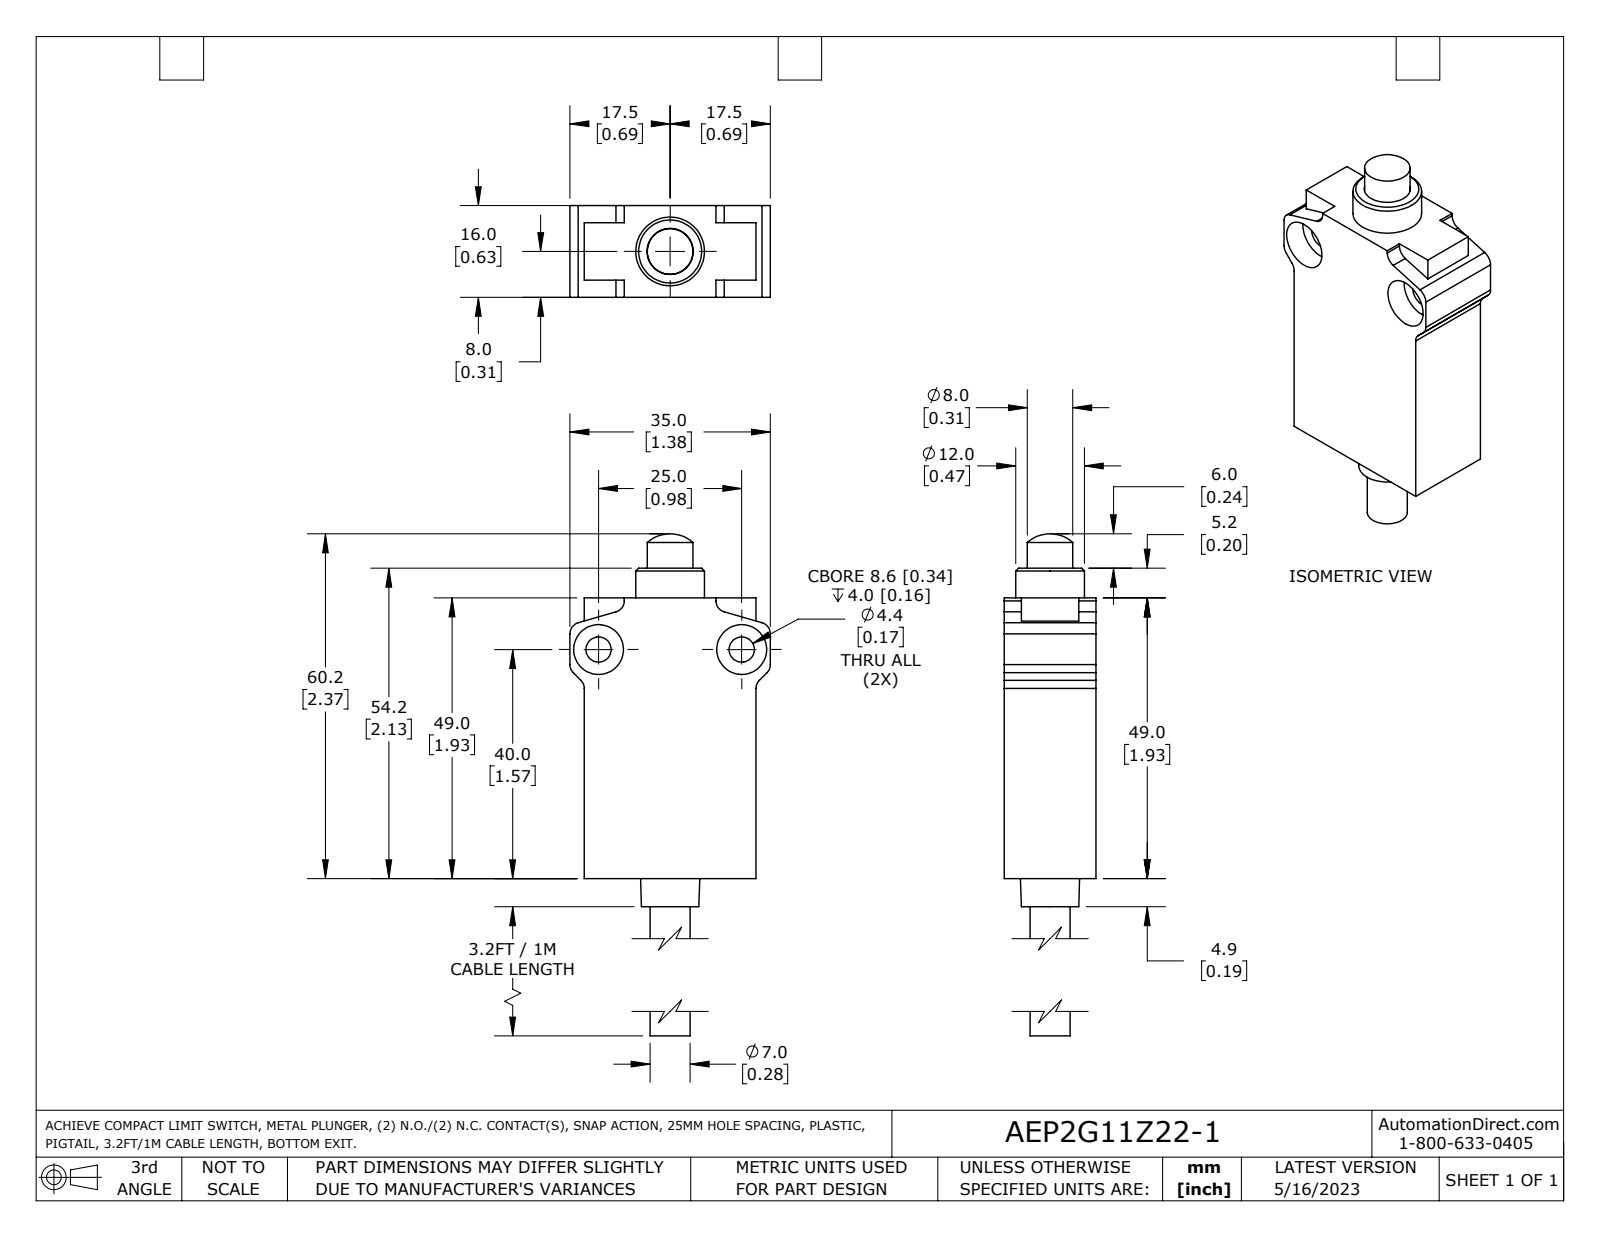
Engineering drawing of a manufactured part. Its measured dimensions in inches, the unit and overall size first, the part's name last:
Units: inches
Overall size (bounding box): 2.957 × 1.378 × 0.63
Round holes (diameter × count): ⌀0.173 ×2, ⌀0.343 ×2, ⌀0.317 ×1
Round bosses / shafts (diameter × count): ⌀0.472 ×1, ⌀0.313 ×1, ⌀0.276 ×1
Partial cylindrical surfaces — rounded edges, fillets, slot ends (radius × count): R0.079 ×8, R0.256 ×1
Main face-to-face distances: 0.63, 1.181, 1.929, 0.157, 0.472, 0.098, 1.28, 0.354, 0.039, 0.315
Hole centre spacings: 0.984
Volume: 1.475 in³ · Surface area: 11.33 in²
Bodies: 1 solid, 76 faces (44 planar, 25 cylindrical, 7 other)
Part name (STEP PRODUCT): AEP2G11Z22-1
STEP written by: SolidWorks 2021 (AUTOMOTIVE_DESIGN)
